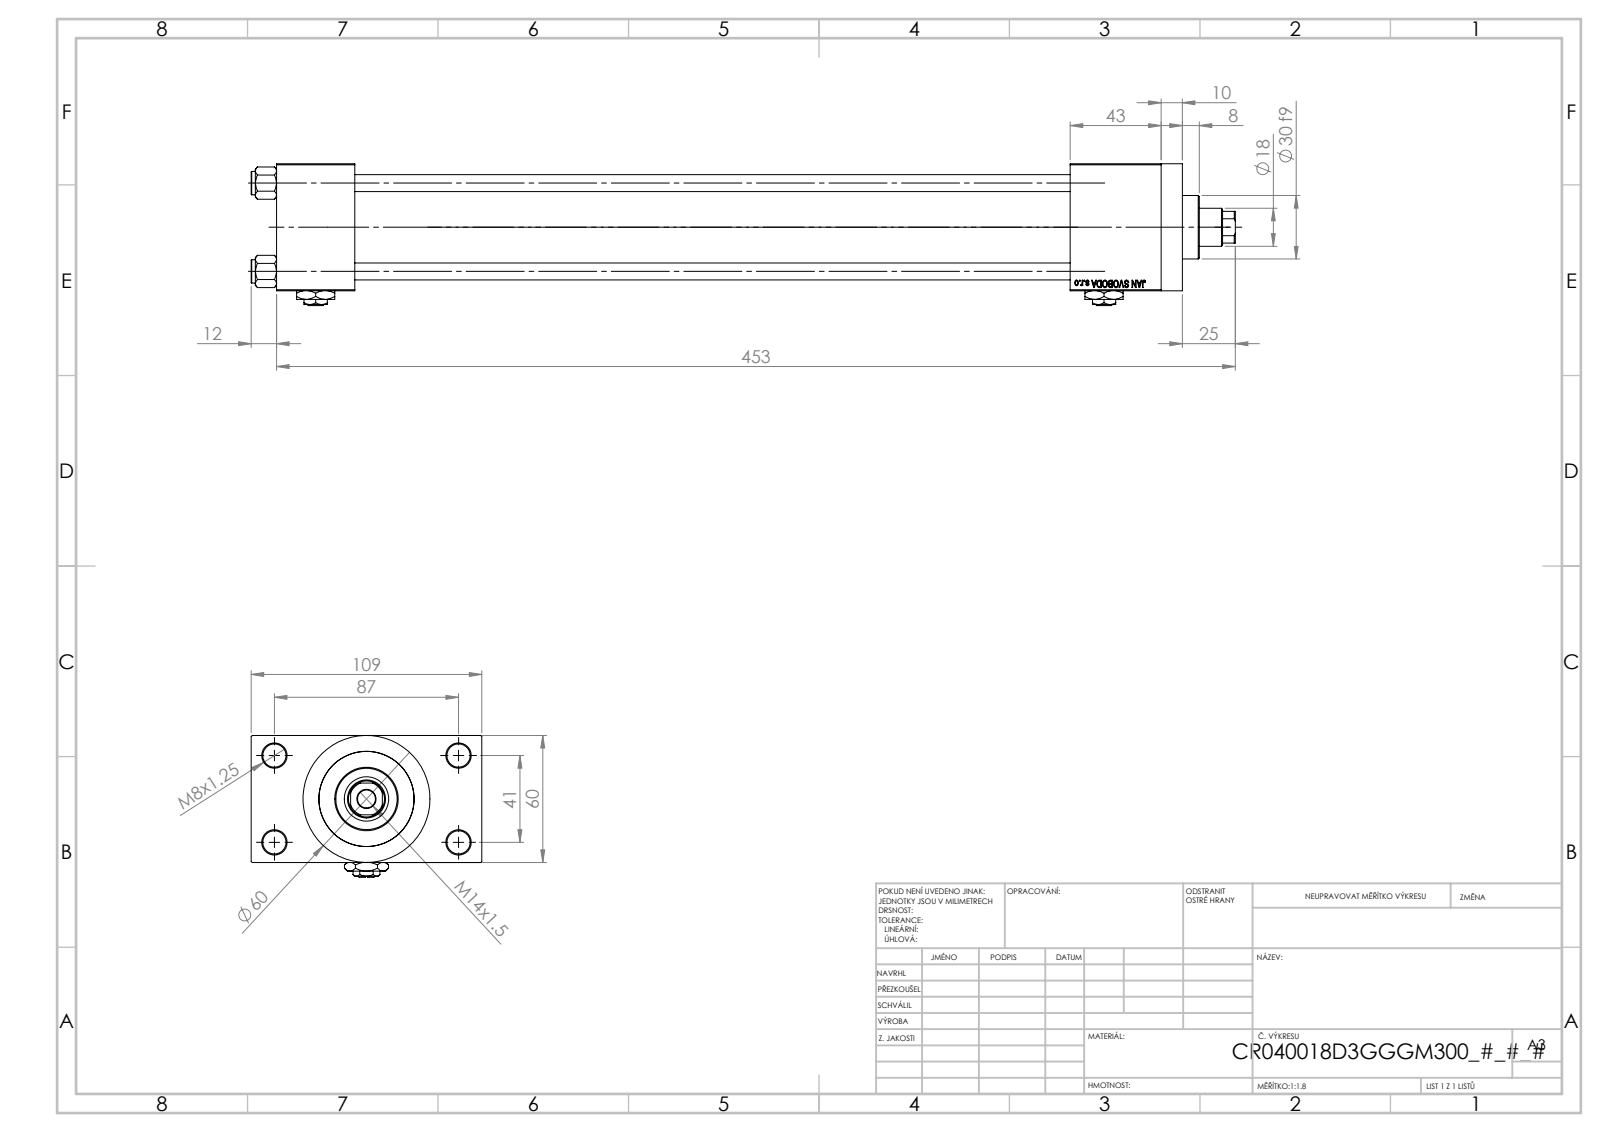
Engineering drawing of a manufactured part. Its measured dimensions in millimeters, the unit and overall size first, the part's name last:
Units: millimetres
Overall size (bounding box): 465 × 109 × 67
Round holes (diameter × count): ⌀8 ×4, ⌀11 ×4, ⌀7 ×2, ⌀16.66 ×2, ⌀24 ×2, ⌀8.5 ×1, ⌀18 ×1, ⌀21 ×1, ⌀31 ×1, ⌀40 ×1, ⌀45 ×1
Round bosses / shafts (diameter × count): ⌀11 ×4, ⌀60 ×1, ⌀46 ×1, ⌀30 ×1
Partial cylindrical surfaces — rounded edges, fillets, slot ends (radius × count): R8.5 ×1
Main face-to-face distances: 60, 24.5, 84.5, 338, 37, 375, 43, 418, 381, 109
Hole centre spacings: 22.65, 29.49, 41.7, 47.15, 48.09, 64.35, 76.49, 41
Volume: 756 615 mm³ · Surface area: 243 547 mm²
Bodies: 13 solids, 1206 faces (546 planar, 100 cylindrical, 560 other)
Part name (STEP PRODUCT): V215CR_VCP_D; V215CR_D_Body; NUT_M5_D; V215CR_D_TYCINKA (+2 more)
STEP written by: SolidWorks 2019 (CONFIG_CONTROL_DESIGN)
